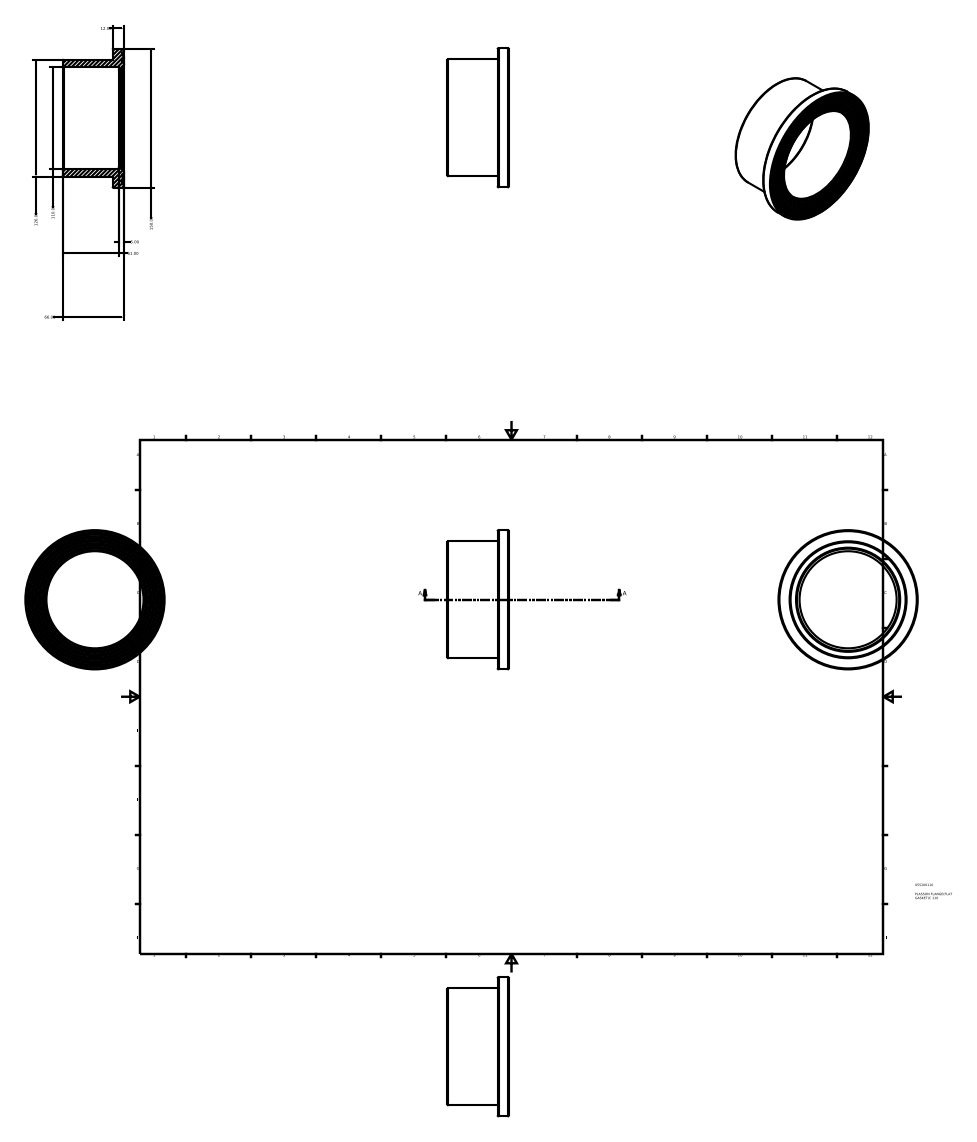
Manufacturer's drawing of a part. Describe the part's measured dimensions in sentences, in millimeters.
The part is named "055200110". Its 3-D file was written by "Autodesk Inventor 2015 (AUTOMOTIVE_DESIGN)". It is 1 solid with 28 faces: 9 planar, 4 cylindrical and 15 other. Overall it measures 150 by 150 by 66 millimeters. Its volume is 254 098 cubic millimeters and its surface area 68 174 square millimeters. Round holes: 1 of diameter 104.5, 1 of diameter 110. Round bosses or shafts: 1 of diameter 150, 1 of diameter 126. The main face-to-face distances are 54, 66, 12, 64.2, 10.2, 1.8, 61, 7, 3.2, 5.
